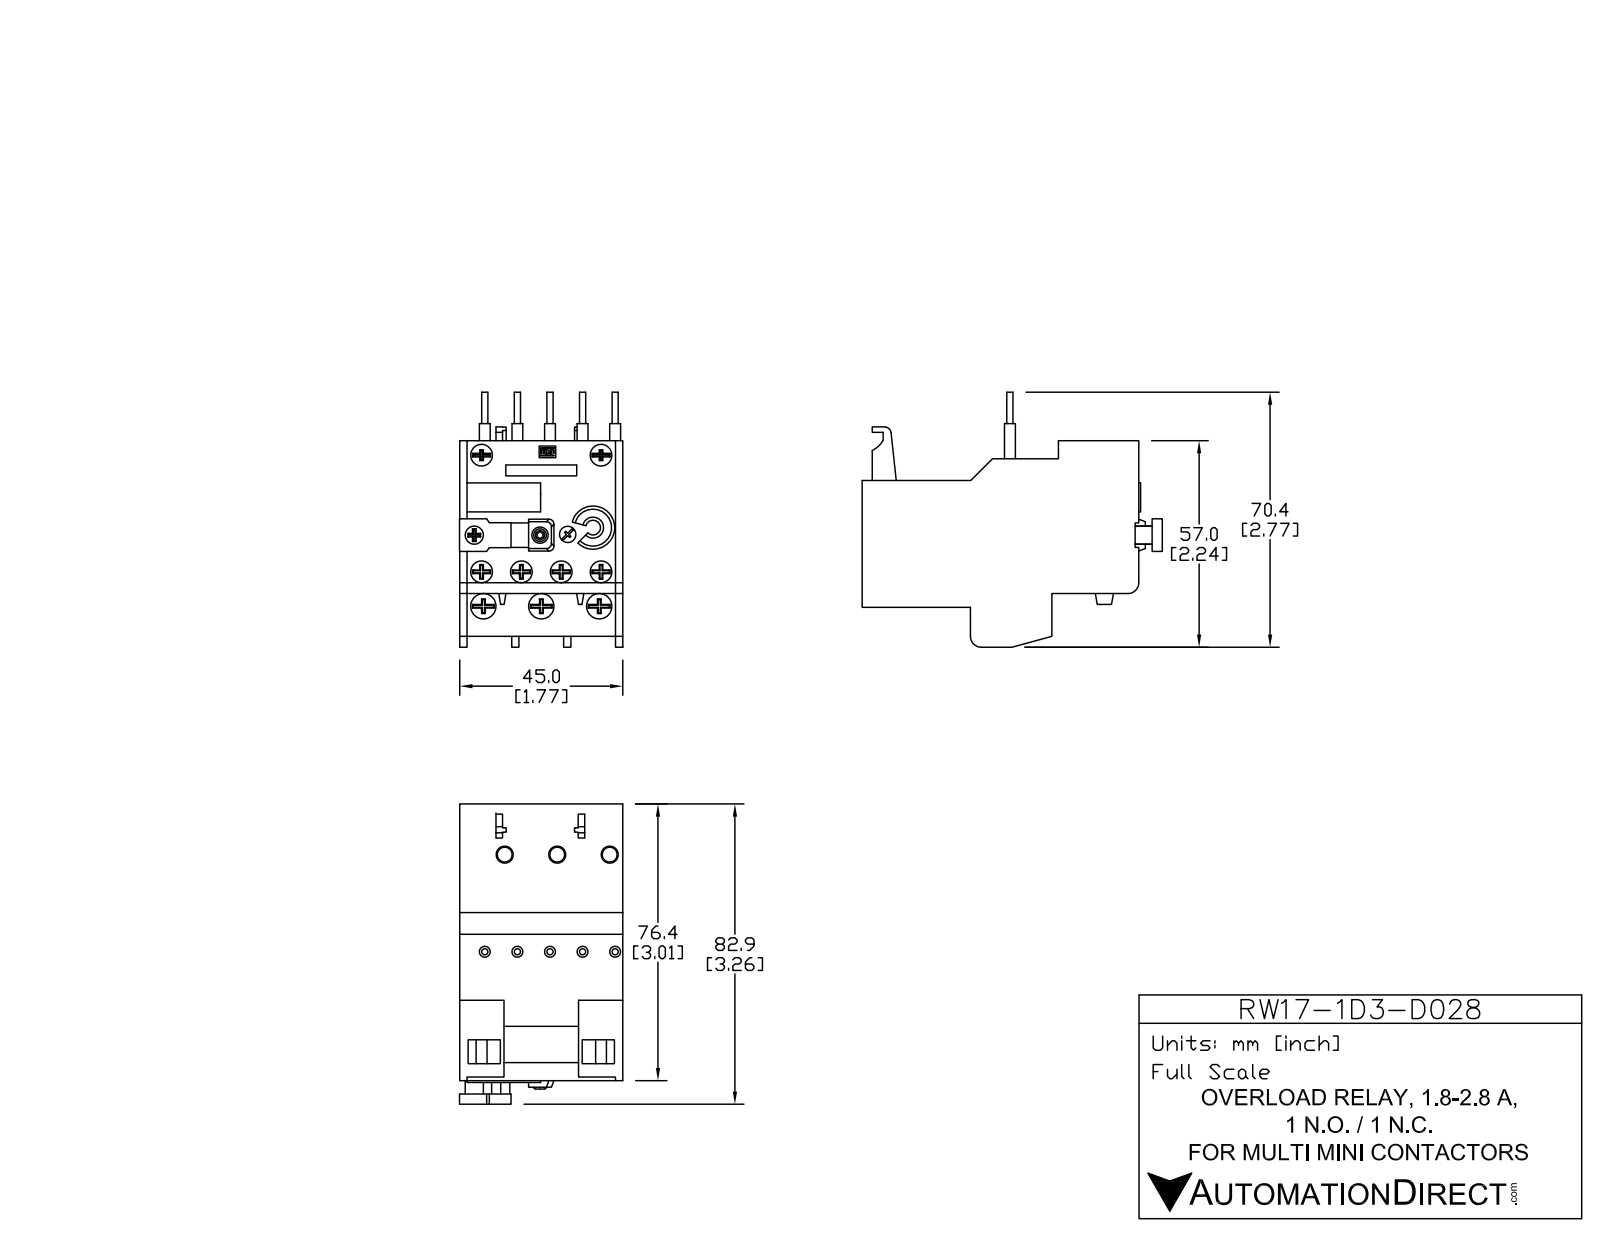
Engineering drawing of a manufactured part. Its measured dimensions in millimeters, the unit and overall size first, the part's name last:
Units: millimetres
Overall size (bounding box): 82.65 × 70.5 × 45.55
Round holes (diameter × count): ⌀6 ×6, ⌀4 ×3, ⌀7 ×3, ⌀7.5 ×3, ⌀4.5 ×1, ⌀4.75 ×1, ⌀5.33 ×1, ⌀5.5 ×1, ⌀10.42 ×1
Round bosses / shafts (diameter × count): ⌀5.5 ×7, ⌀3 ×7, ⌀1.75 ×5, ⌀5.6 ×2, ⌀3.25 ×2, ⌀6.42 ×1, ⌀6.15 ×1, ⌀4.75 ×1
Partial cylindrical surfaces — rounded edges, fillets, slot ends (radius × count): R0.5 ×20, R0.25 ×12, R1 ×9, R4.52 ×6, R5.86 ×4, R7.86 ×4, R1.5 ×3, R1.25 ×2
Main face-to-face distances: 45.5, 1.5, 10.85, 11, 76.4, 35, 1.42, 74.98, 74.9, 6
Hole centre spacings: 15, 8.55, 10.75, 30, 10.57, 11.86, 14.25, 21.35
Volume: 127 454 mm³ · Surface area: 34 704 mm²
Bodies: 18 solids, 756 faces (515 planar, 214 cylindrical, 27 other)
Part name (STEP PRODUCT): RW17D-1D3-D028
STEP written by: SolidWorks 2013 (AUTOMOTIVE_DESIGN)
